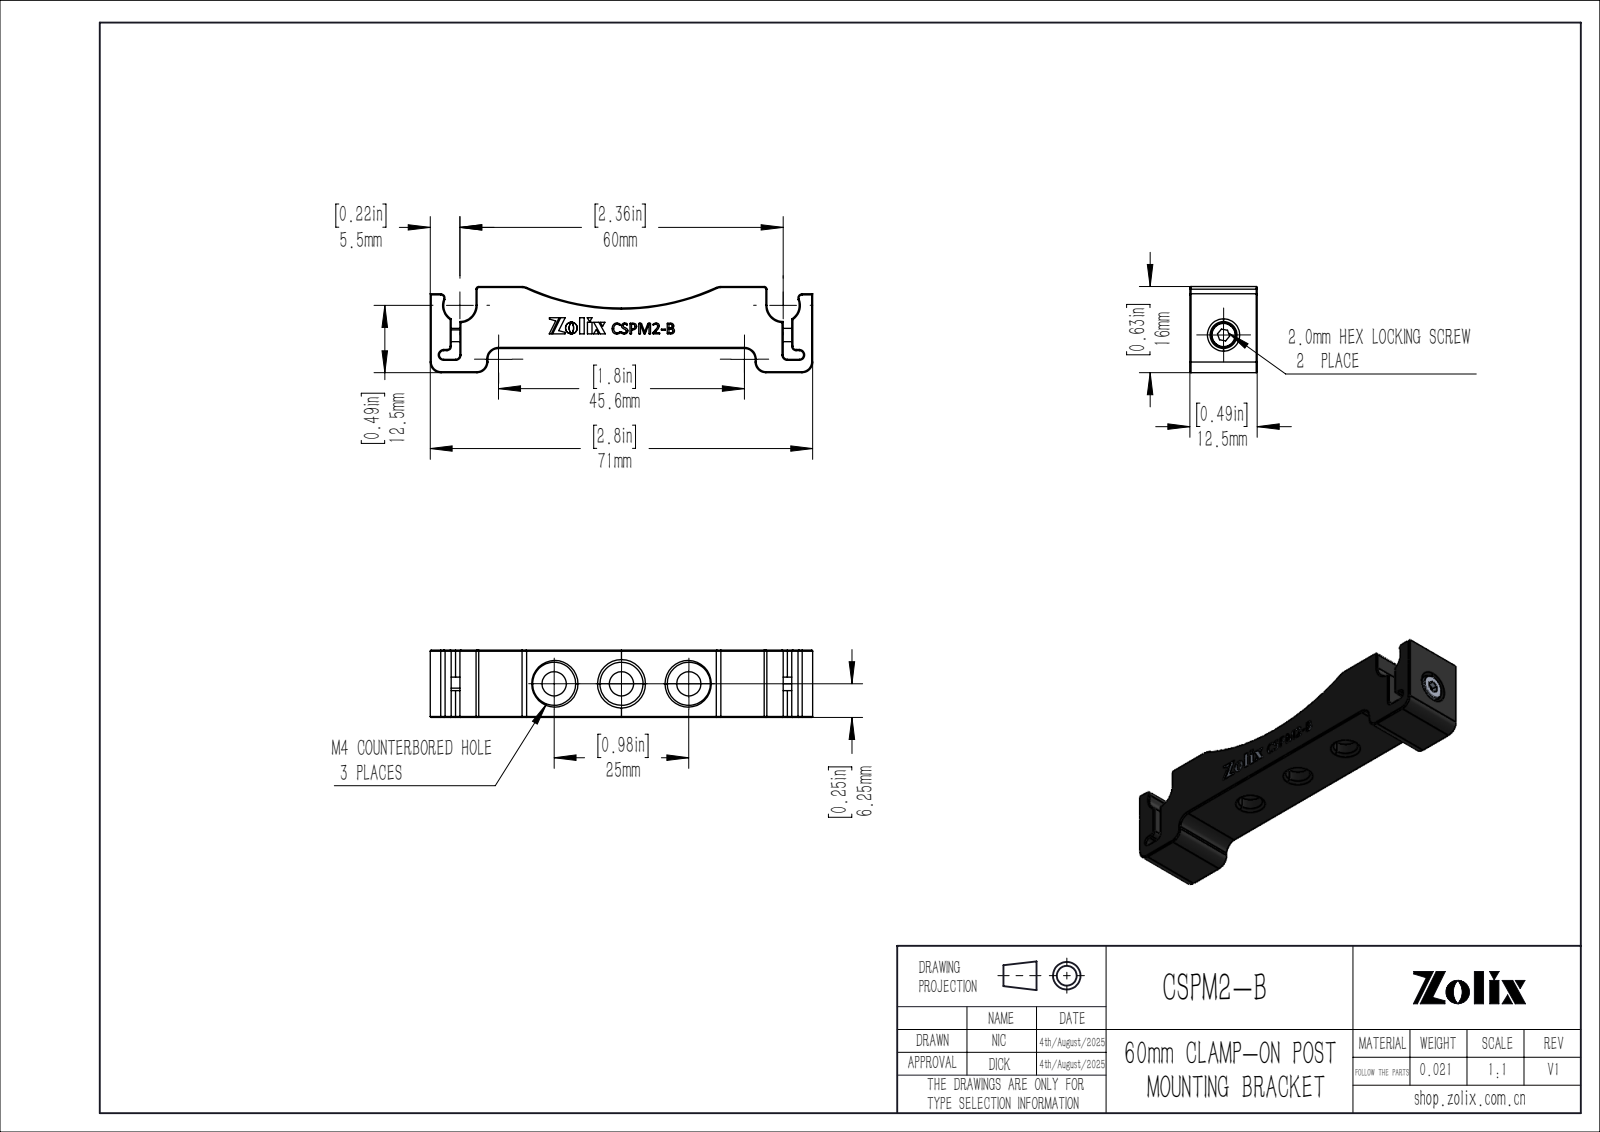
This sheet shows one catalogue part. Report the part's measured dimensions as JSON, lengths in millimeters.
{"part_name": "CSPM2-B", "step_written_by": "SolidWorks 2020 (CONFIG_CONTROL_DESIGN)", "units": "millimeters", "bodies": {"solids": 3, "faces": 510, "planar": 266, "cylindrical": 98, "other": 146}, "overall_size": [71, 15.99, 12.5], "volume_mm3": 7722, "surface_area_mm2": 5075, "round_holes": [[4.5, 3], [8, 3], [2.05, 1], [2.9, 1], [5, 1]], "round_bosses_or_shafts": [[4.5, 1], [2.5, 1]], "partial_cylinders_radius": [[0.2, 32], [0.8, 8], [2, 8], [0.5, 2], [3, 2], [42.5, 1]], "face_to_face_distances": [12.5, 4.5, 11.5, 2.5, 16, 5.5, 65.5, 71, 1.6, 3.9], "hole_center_spacings": [12.5, 25]}
